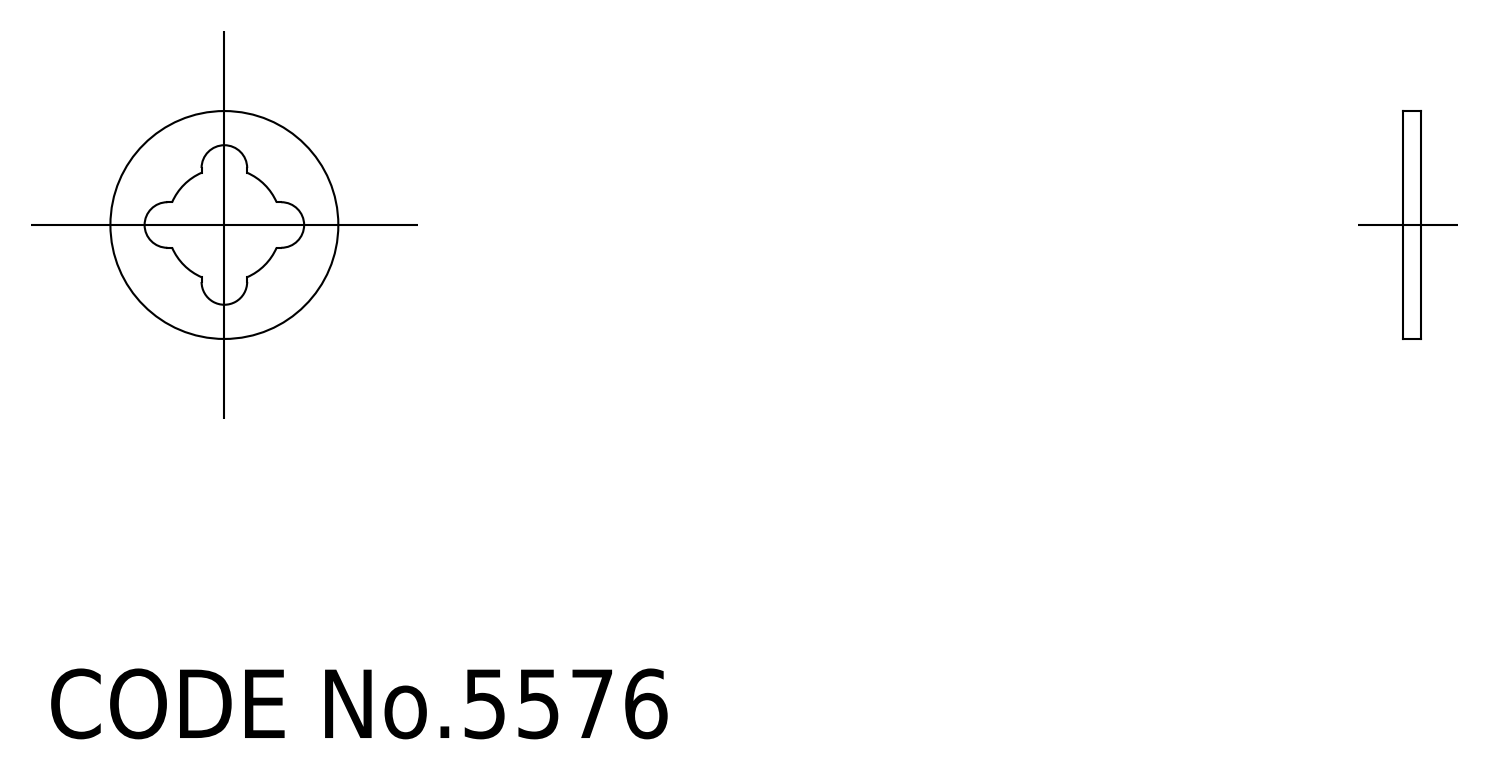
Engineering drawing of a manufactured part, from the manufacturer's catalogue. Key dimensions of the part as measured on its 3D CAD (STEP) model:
Part name (STEP PRODUCT): washer
STEP written by: CADfix (AUTOMOTIVE_DESIGN)
Units: millimetres
Bodies: 1 solid, 20 faces (0 planar, 0 cylindrical, 20 other)
Overall size (bounding box): 10 × 10 × 0.8
Volume: 42 mm³ · Surface area: 147 mm²
